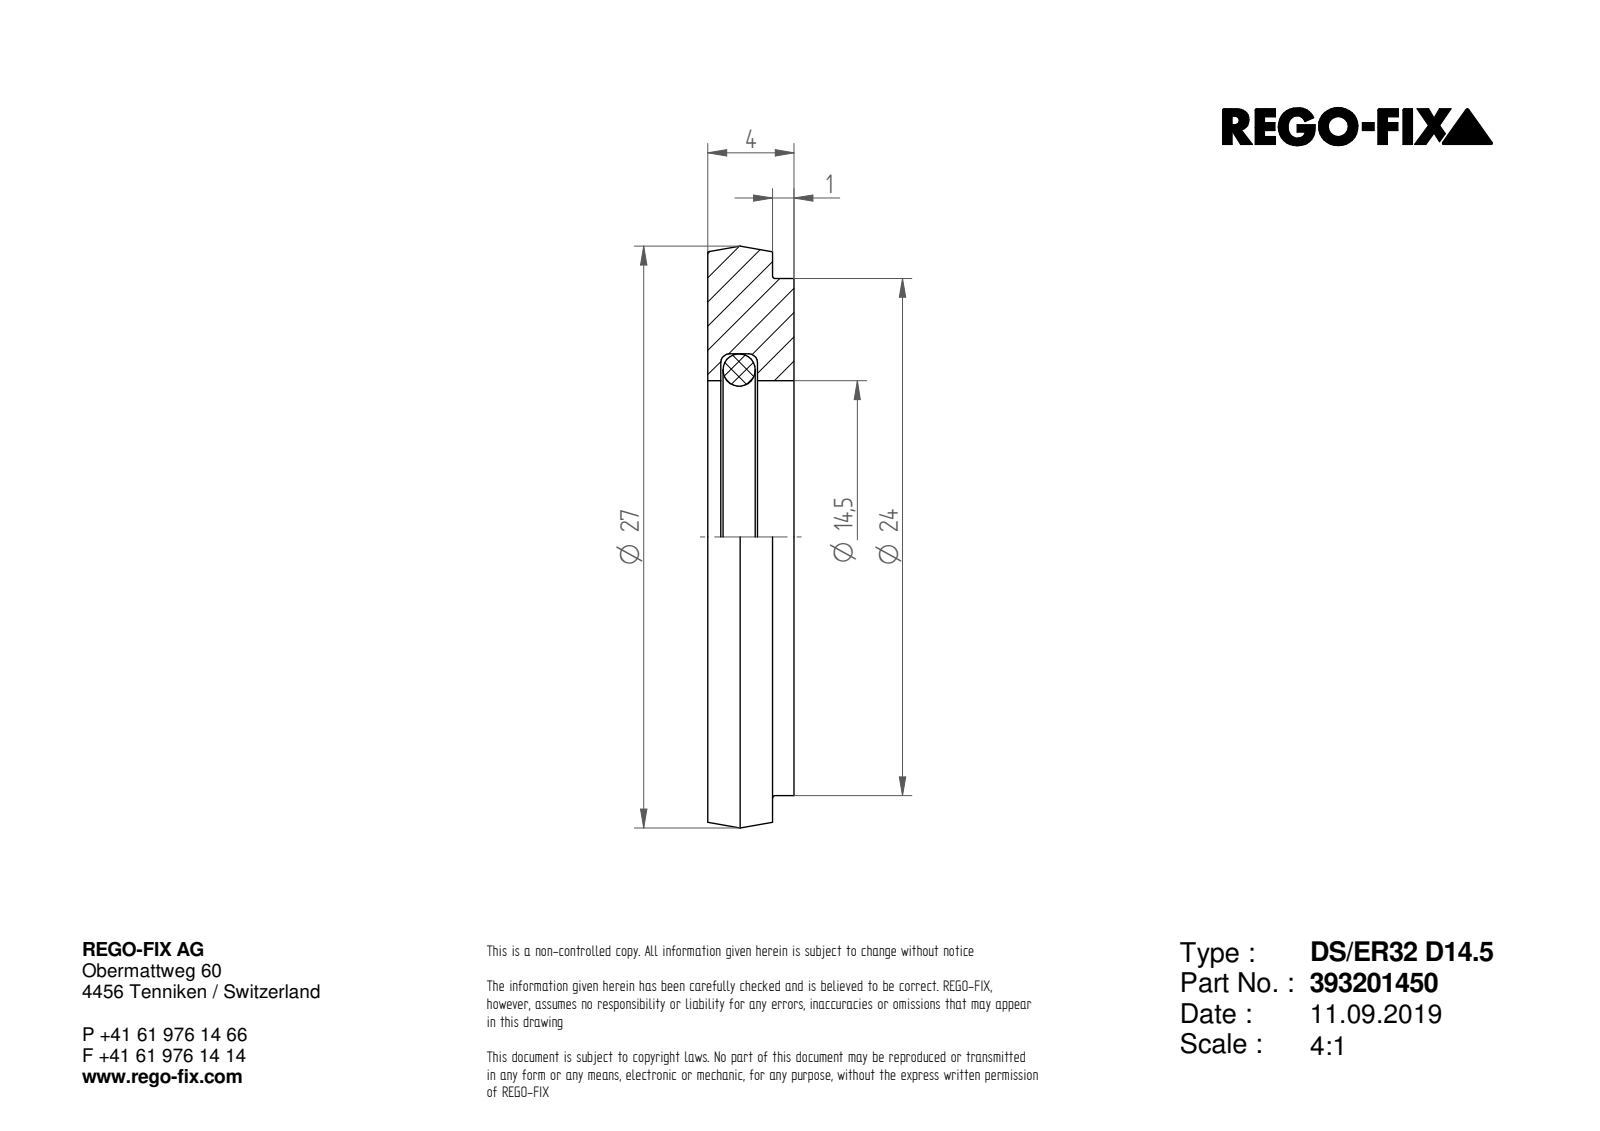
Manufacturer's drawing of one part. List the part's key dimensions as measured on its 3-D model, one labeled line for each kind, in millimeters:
Part name (STEP PRODUCT): NOCUT
STEP written by: SIEMENS PLM Software Solid Edge ST10 (AUTOMOTIVE_DESIGN)
Units: millimetres
Bodies: 1 solid, 7 faces (3 planar, 3 cylindrical, 1 other)
Overall size (bounding box): 27 × 27 × 4
Volume: 1 510 mm³ · Surface area: 1 324 mm²
Round holes (diameter × count): ⌀14.5 ×1
Round bosses / shafts (diameter × count): ⌀27 ×1, ⌀24 ×1
Main face-to-face distances: 4, 1, 3
